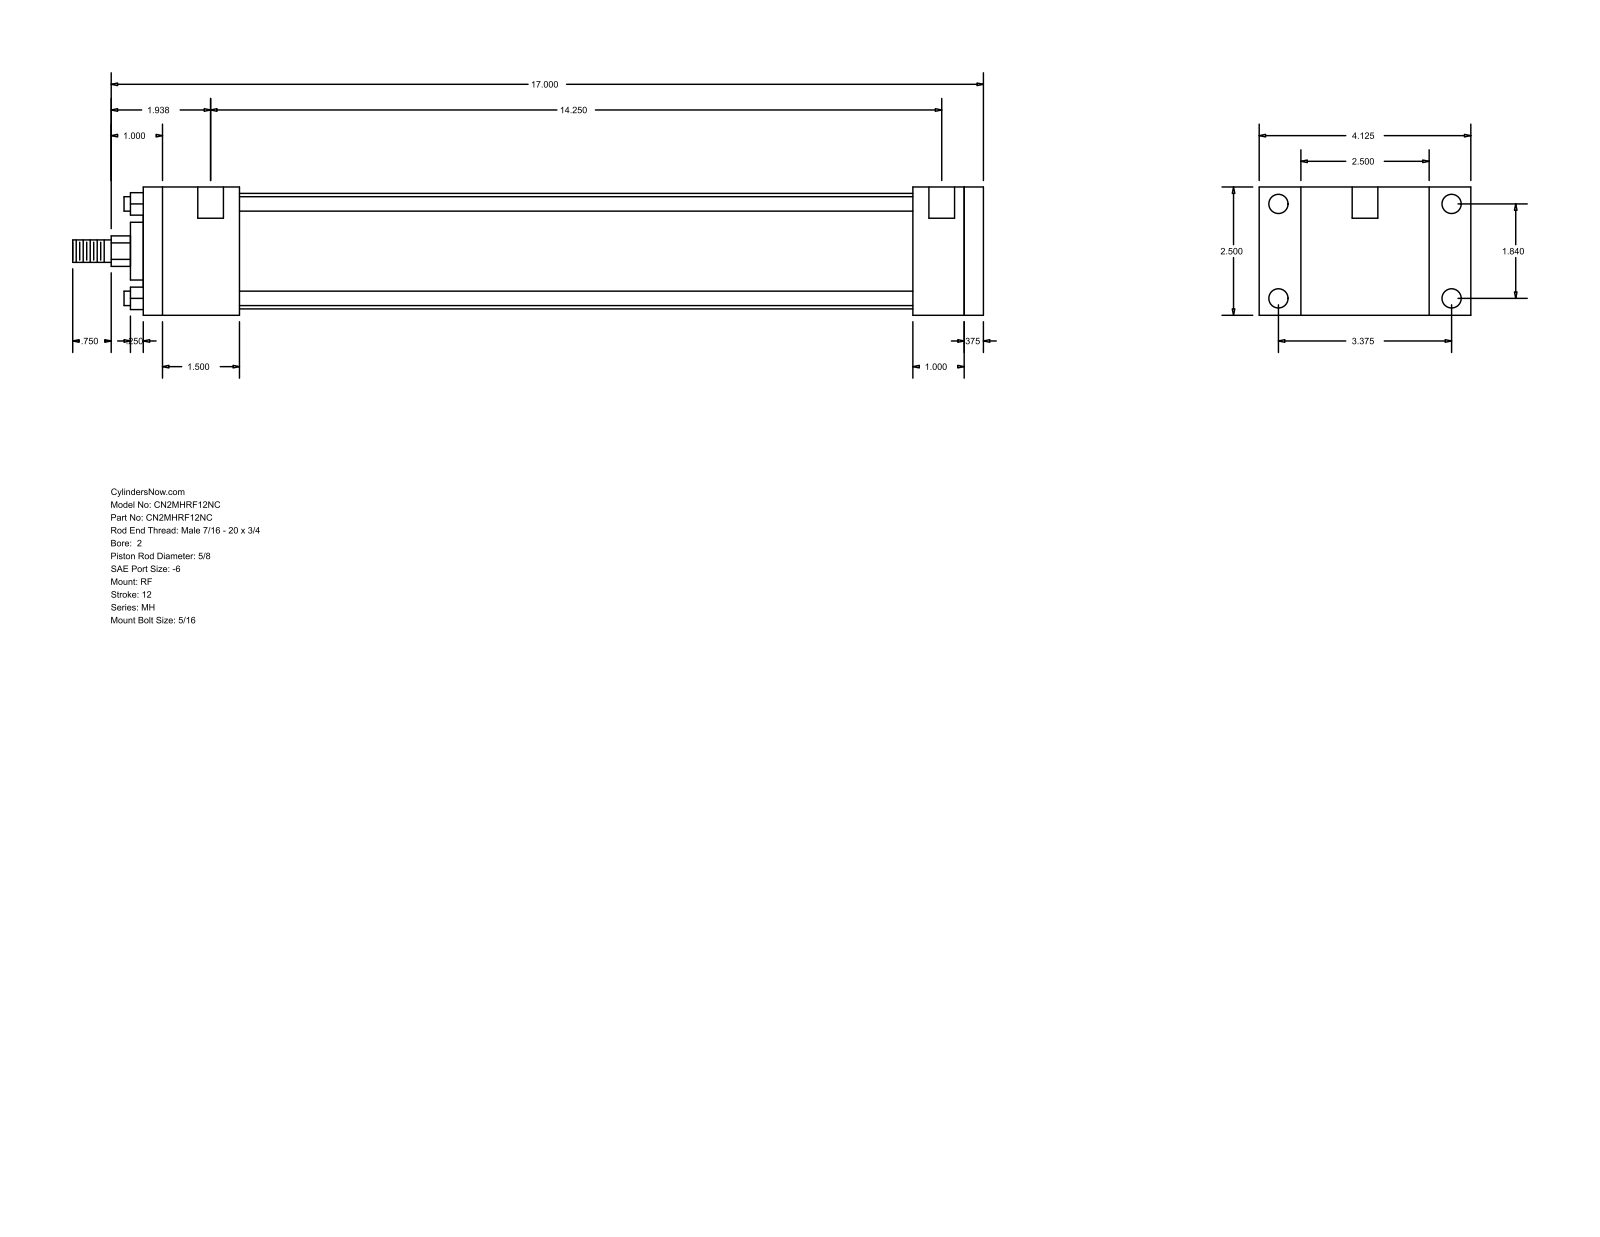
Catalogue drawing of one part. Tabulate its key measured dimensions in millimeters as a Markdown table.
| quantity | value |
| --- | --- |
| part name | MH_RF__0200_0.625 |
| STEP written by | GSSL Pune (CONFIG_CONTROL_DESIGN) |
| units | millimeters |
| bodies | 0 solids, 92 faces (64 planar, 28 cylindrical, 0 other) |
| overall size | 450.85 × 104.78 × 63.5 |
| round holes (diameter × count) | 5.56 × 4, 9.53 × 4, 12.7 × 2 |
| round bosses / shafts (diameter × count) | 7.14 × 4, 57.15 × 1, 28.57 × 1, 15.88 × 1, 11.11 × 1 |
| partial cylindrical surfaces (radius × count) | 7.54 × 1 |
| main face-to-face distances | 63.5, 415.92, 9.53, 406.39, 47.62, 381, 333.38, 358.77, 368.3, 25.39 |
| hole center spacings | 46.74, 85.72, 97.63, 369.89, 3.18, 4.76, 361.95, 365.13 |
